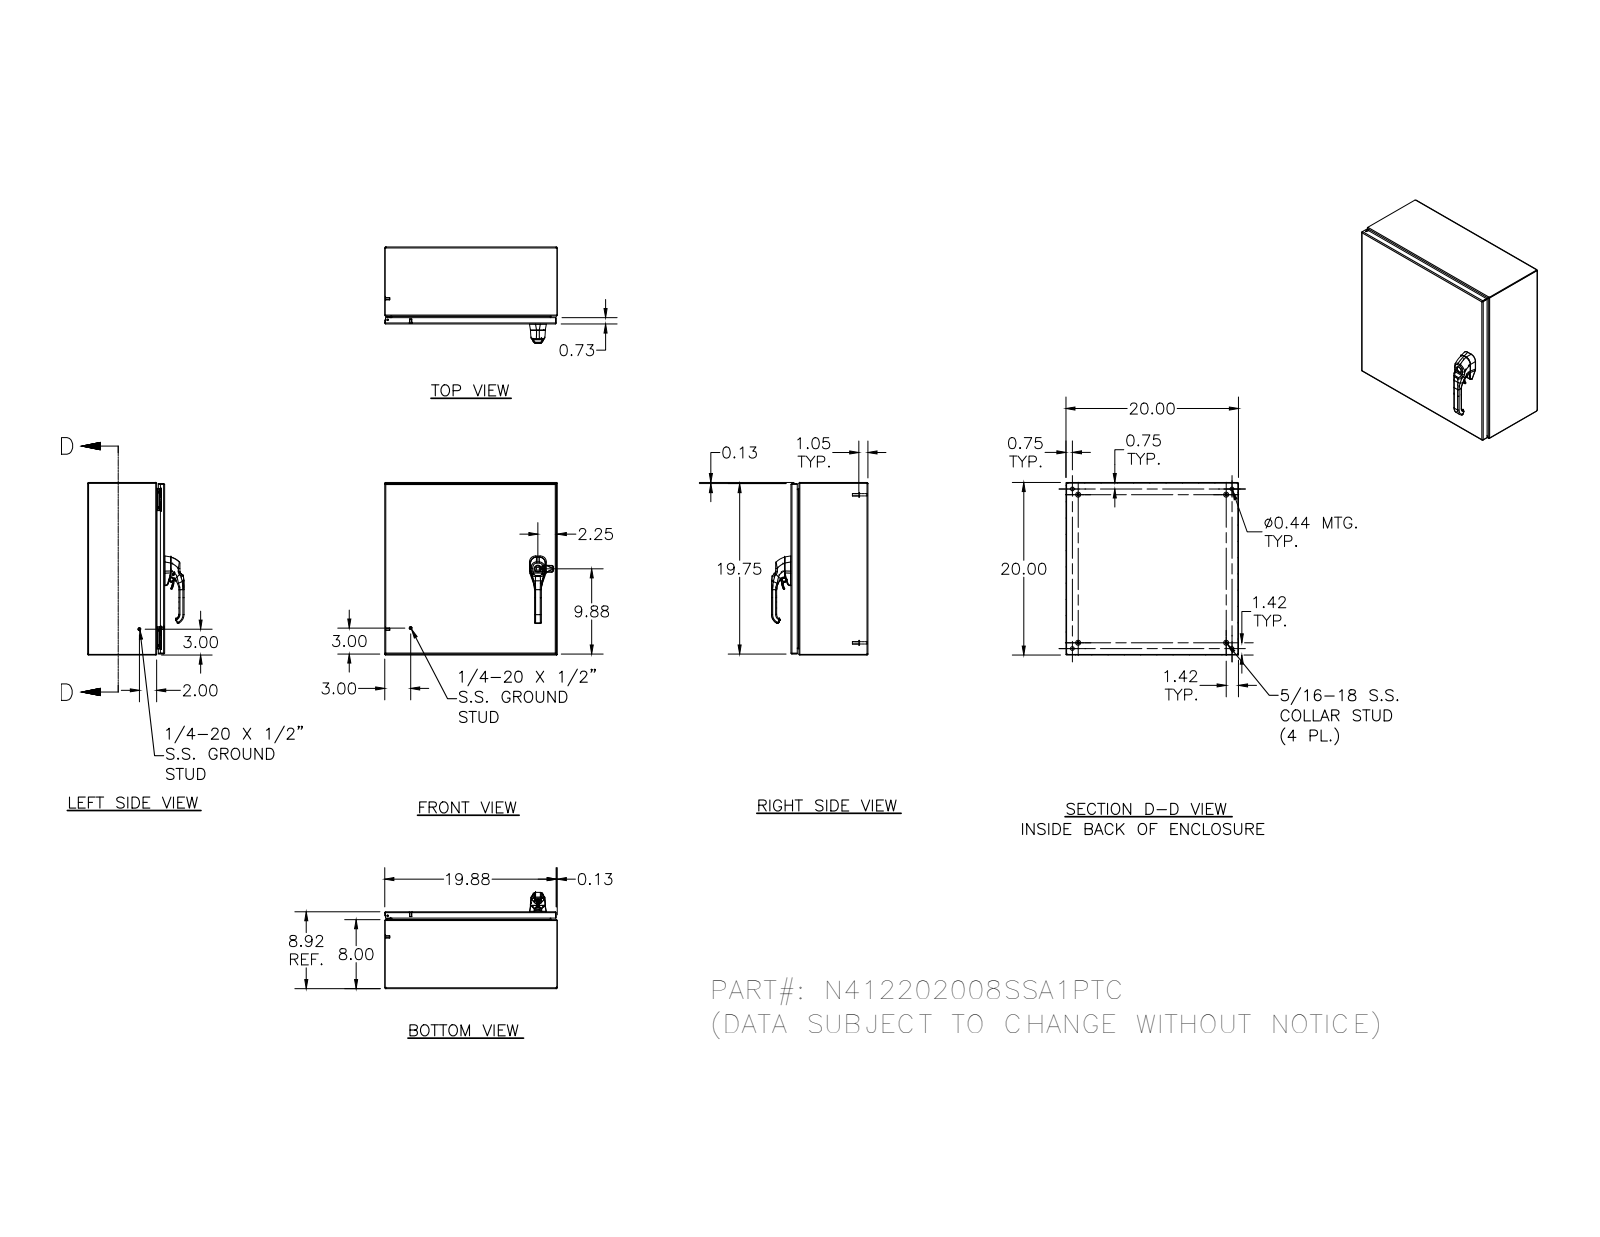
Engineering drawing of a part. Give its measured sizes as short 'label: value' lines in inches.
name: N412202008SSA1PTC; N412202008SSA1PTCBKP; N4122020SSA1PTCLID; HFW328176 (+8 more)
written by: Autodesk Inventor 2012 (AUTOMOTIVE_DESIGN)
unit: in
bodies: 41 solids, 2784 faces (882 planar, 1037 cylindrical, 865 other)
size: 20 × 20 × 11.166
volume: 125.6 in³; area: 3 314 in²
holes: 5× ⌀0.188, 4× ⌀0.093, 4× ⌀0.152, 4× ⌀0.167, 4× ⌀0.172, 4× ⌀0.437, 3× ⌀0.213, 3× ⌀0.281, 2× ⌀0.156, 2× ⌀0.315, 2× ⌀0.402, 2× ⌀0.413
bosses: 10× ⌀0.25, 4× ⌀0.563, 4× ⌀0.36, 4× ⌀0.32, 4× ⌀0.3, 4× ⌀0.275, 4× ⌀0.256, 4× ⌀0.164
rounds: 174× R0.02, 101× R0.012, 30× R0.031, 26× R0.05, 21× R0.019, 20× R0.105, 18× R0.016, 14× R0.079
face distances: 0.074, 8.843, 19.926, 8.917, 8.769, 19.852, 20, 7.926, 0.917, 0.739
hole spacings: 15.996, 18.5, 18.872, 0.017, 0.66, 16.004, 16.656, 0.019
